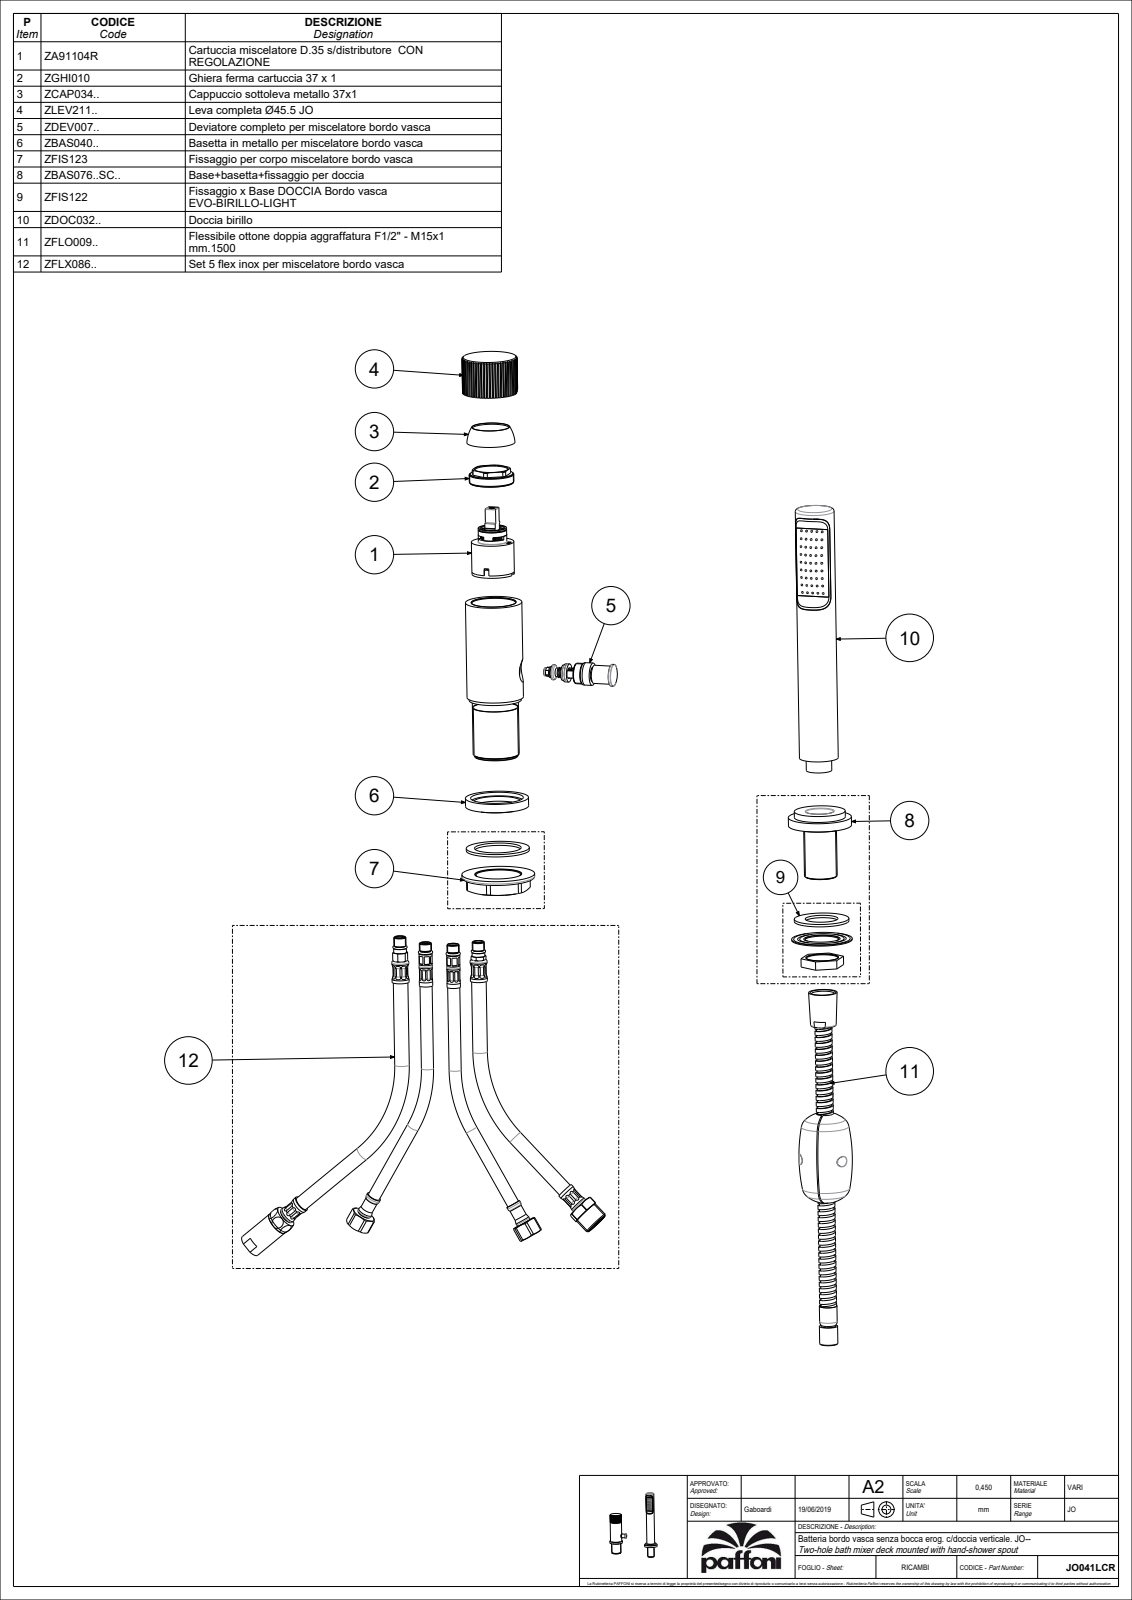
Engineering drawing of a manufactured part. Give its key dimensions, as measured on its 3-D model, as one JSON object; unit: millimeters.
{"part_name": "JO041LCR", "step_written_by": "CREO PARAMETRIC BY PTC INC, 2020044 (CONFIG_CONTROL_DESIGN)", "units": "millimeters", "bodies": {"solids": 2, "faces": 1447, "planar": 770, "cylindrical": 471, "other": 206}, "overall_size": [215, 197, 52], "volume_mm3": 199818, "surface_area_mm2": 109458, "round_holes": [[1.5, 45], [7, 6], [4, 2], [3, 1], [3.1, 1], [3.3, 1], [4.3, 1], [4.5, 1], [5, 1], [5.5, 1], [6, 1], [7.2, 1]], "round_bosses_or_shafts": [[52, 1], [46.5, 1], [44.2, 1], [43, 1], [42, 1], [38, 1], [35, 1], [34.8, 1]], "partial_cylinders_radius": [[0.5, 27], [0.15, 11], [0.3, 4], [1, 2], [7.8, 2], [9.8, 2], [10, 2], [3.9, 1]], "face_to_face_distances": [2, 116.1, 5, 208, 10, 0.5, 213, 2.5, 3, 60.8], "hole_center_spacings": [7.91, 13.76, 20.01, 6.5, 13, 26.39, 4.5, 19.5]}
